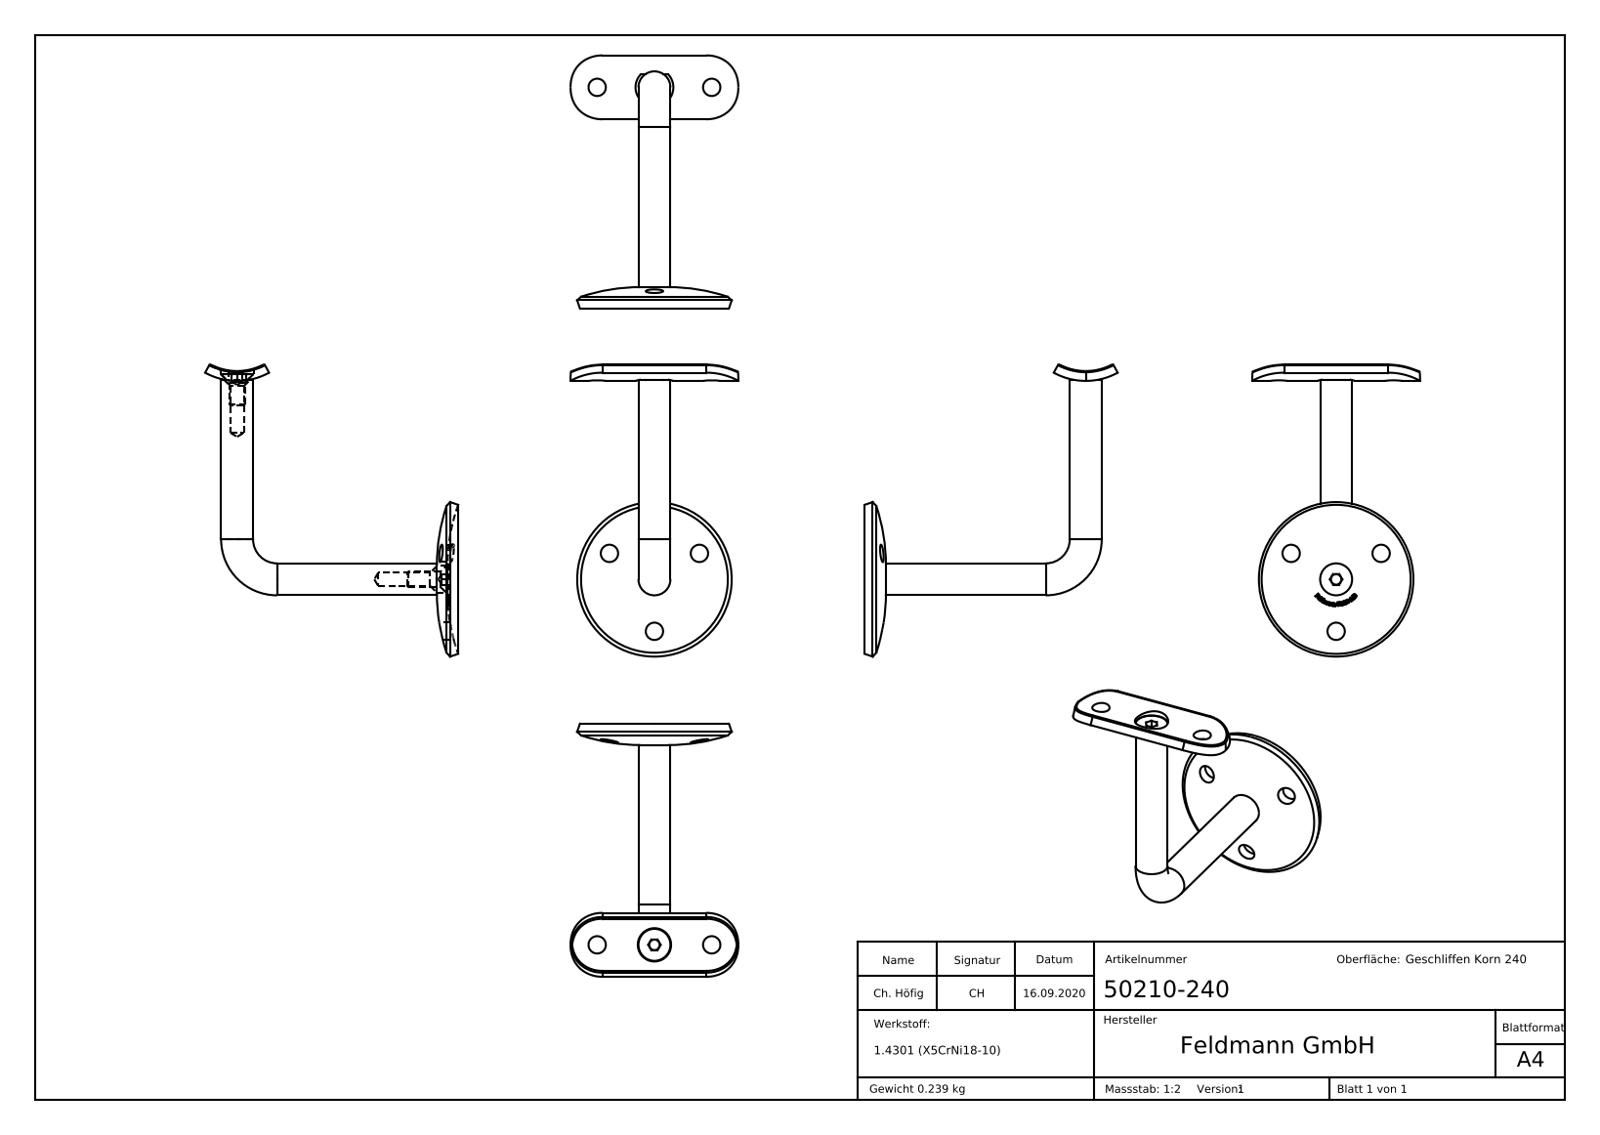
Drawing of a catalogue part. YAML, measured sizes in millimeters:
part_name: "50210-240 Teil3_50210-240 Teil3; DIN-7991 M3-M10_DIN7991 M6x16; 50210-240 Teil2_50210-240 Teil2; 50210-240 (+6 more)"
step_written_by: "SolidWorks 2018 (CONFIG_CONTROL_DESIGN)"
units: millimeters
bodies: {solids: 5, faces: 326, planar: 128, cylindrical: 41, other: 157}
overall_size: [109.65, 95, 63]
volume: 30211
surface_area: 16405
round_holes:
  - {diameter: 6.5, count: 5}
  - {diameter: 5, count: 2}
  - {diameter: 10.5, count: 1}
  - {diameter: 12.5, count: 1}
round_bosses_or_shafts:
  - {diameter: 12, count: 2}
  - {diameter: 6, count: 2}
partial_cylinders:
  - {radius: 12, count: 4}
  - {radius: 0.5, count: 2}
  - {radius: 7.1, count: 1}
  - {radius: 21.2, count: 1}
  - {radius: 24.9, count: 1}
face_to_face_distances: [2.2, 4, 4.8, 16, 11.2, 9.8, 12, 73, 77, 77.8]
hole_center_spacings: [19.5, 33.78, 21.5, 43]
